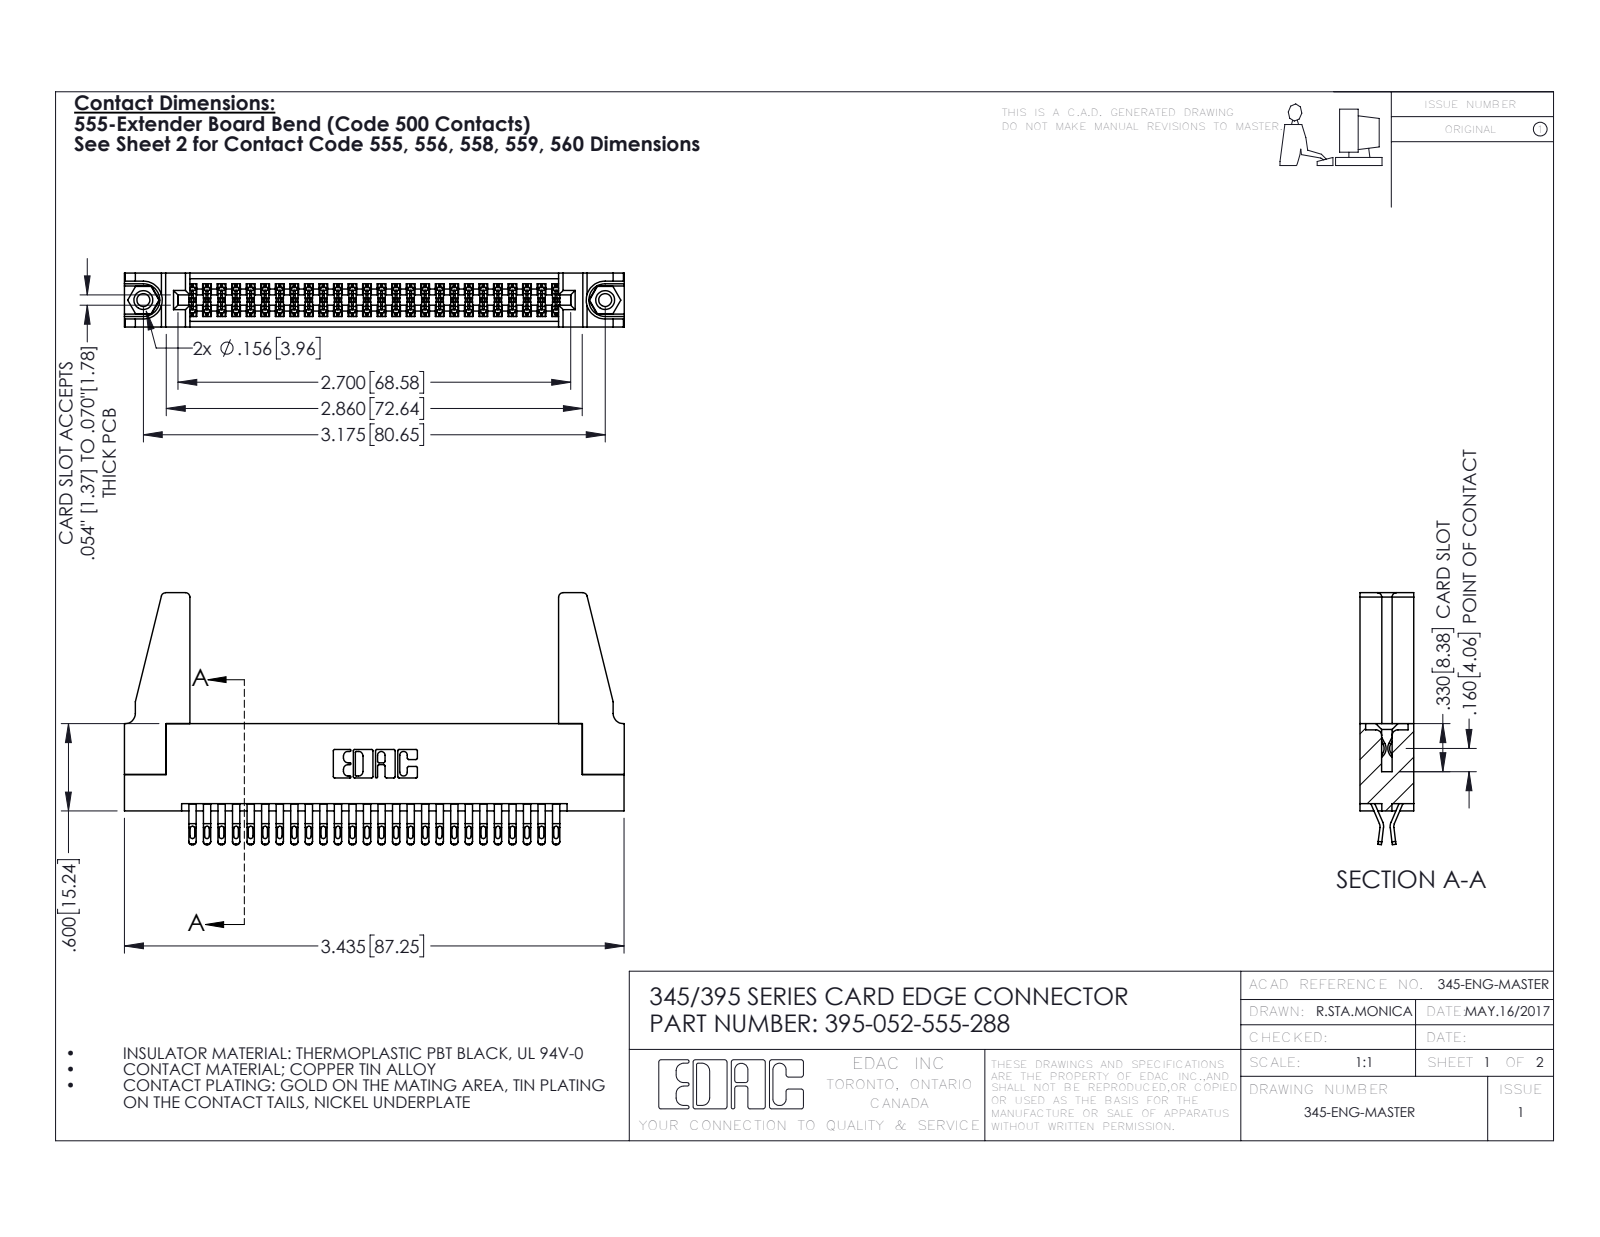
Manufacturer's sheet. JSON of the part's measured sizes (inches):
{"part_name": "395-052-555-288; 345 Part_Flush Mounting Lugs - 0.156 Dia-TH; 345-250-001_345-250-001-102; 345-292-001_555 Tail (+1 more)", "step_written_by": "SolidWorks 2016 (CONFIG_CONTROL_DESIGN)", "units": "inches", "bodies": {"solids": 57, "faces": 3162, "planar": 1764, "cylindrical": 1382, "other": 16}, "overall_size": [3.436, 1.732, 0.37], "volume_in3": 0.716, "surface_area_in2": 24.6, "round_holes": [[0.089, 2], [0.125, 2], [0.156, 2], [0.064, 1]], "round_bosses_or_shafts": [[0.155, 2]], "partial_cylinders_radius": [[0.016, 130], [0.02, 104], [0.006, 78], [0.01, 22], [0.03, 8], [0.007, 6], [0.031, 6], [0.026, 3]], "face_to_face_distances": [0.072, 0.298, 0.37, 0.2, 0.025, 0.098, 0.272, 0.225, 0.175, 0.149], "hole_center_spacings": [0.27, 2.94, 3.175]}
